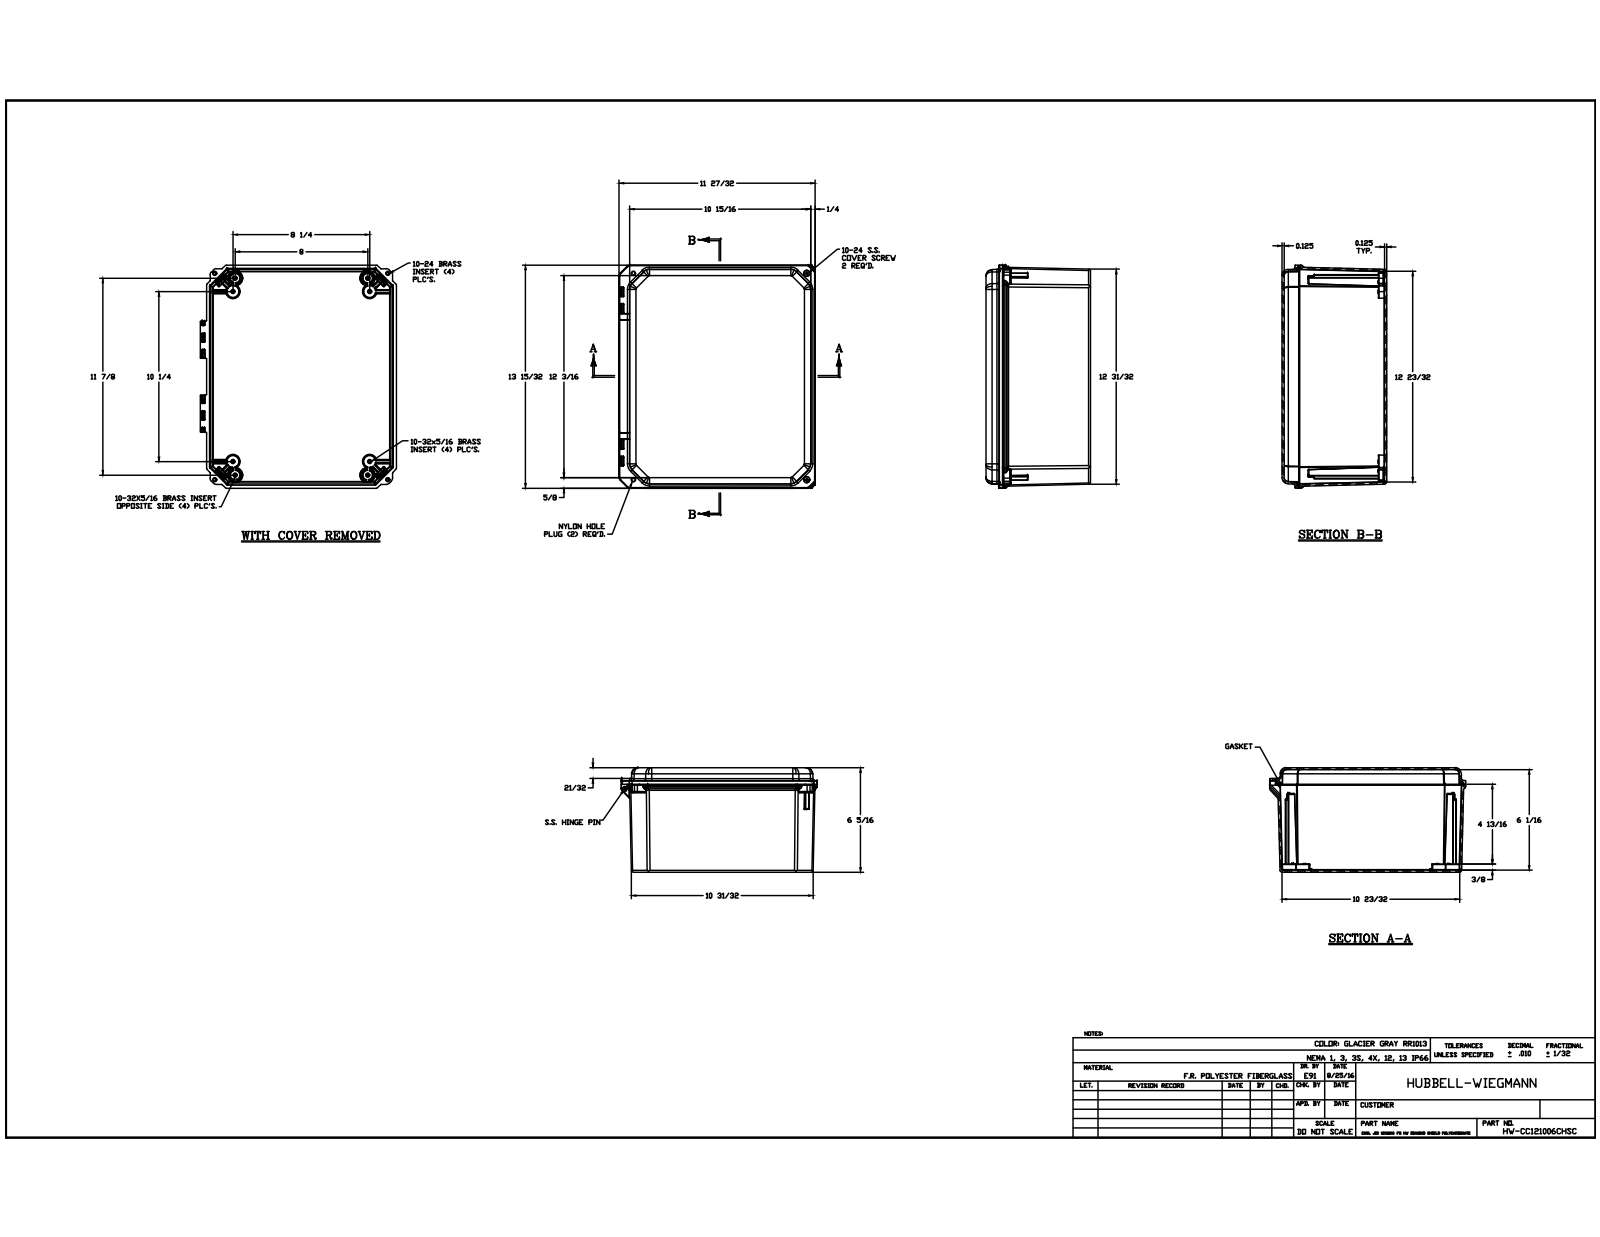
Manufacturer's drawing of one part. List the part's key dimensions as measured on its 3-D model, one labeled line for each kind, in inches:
Part name (STEP PRODUCT): HW-CC121006CHSC; DS121006BOX; BRASS INSERT-(; BRASS INSERT-(_1 (+7 more)
STEP written by: Autodesk Inventor 2017 (CONFIG_CONTROL_DESIGN)
Units: inches
Bodies: 22 solids, 2015 faces (549 planar, 752 cylindrical, 714 other)
Overall size (bounding box): 13.458 × 11.831 × 6.312
Volume: 83.66 in³ · Surface area: 1 240 in²
Round holes (diameter × count): ⌀0.156 ×11, ⌀0.152 ×8, ⌀0.219 ×4, ⌀0.252 ×4, ⌀0.312 ×4, ⌀0.15 ×2, ⌀0.137 ×1
Round bosses / shafts (diameter × count): ⌀0.246 ×11, ⌀0.87 ×4, ⌀0.45 ×2, ⌀0.209 ×2, ⌀0.199 ×2, ⌀0.135 ×1
Partial cylindrical surfaces — rounded edges, fillets, slot ends (radius × count): R0.01 ×188, R0.005 ×94, R0.02 ×59, R0.03 ×38, R0.125 ×29, R0.03 ×24, R0.09 ×24, R0.25 ×24
Main face-to-face distances: 0.125, 6.187, 6.312, 6.062, 0.139, 0.14, 0.14, 5.531, 0.656, 1
Hole centre spacings: 8.166, 9.417, 0.824, 1.261, 9.231, 11.065, 11.406, 12.228
